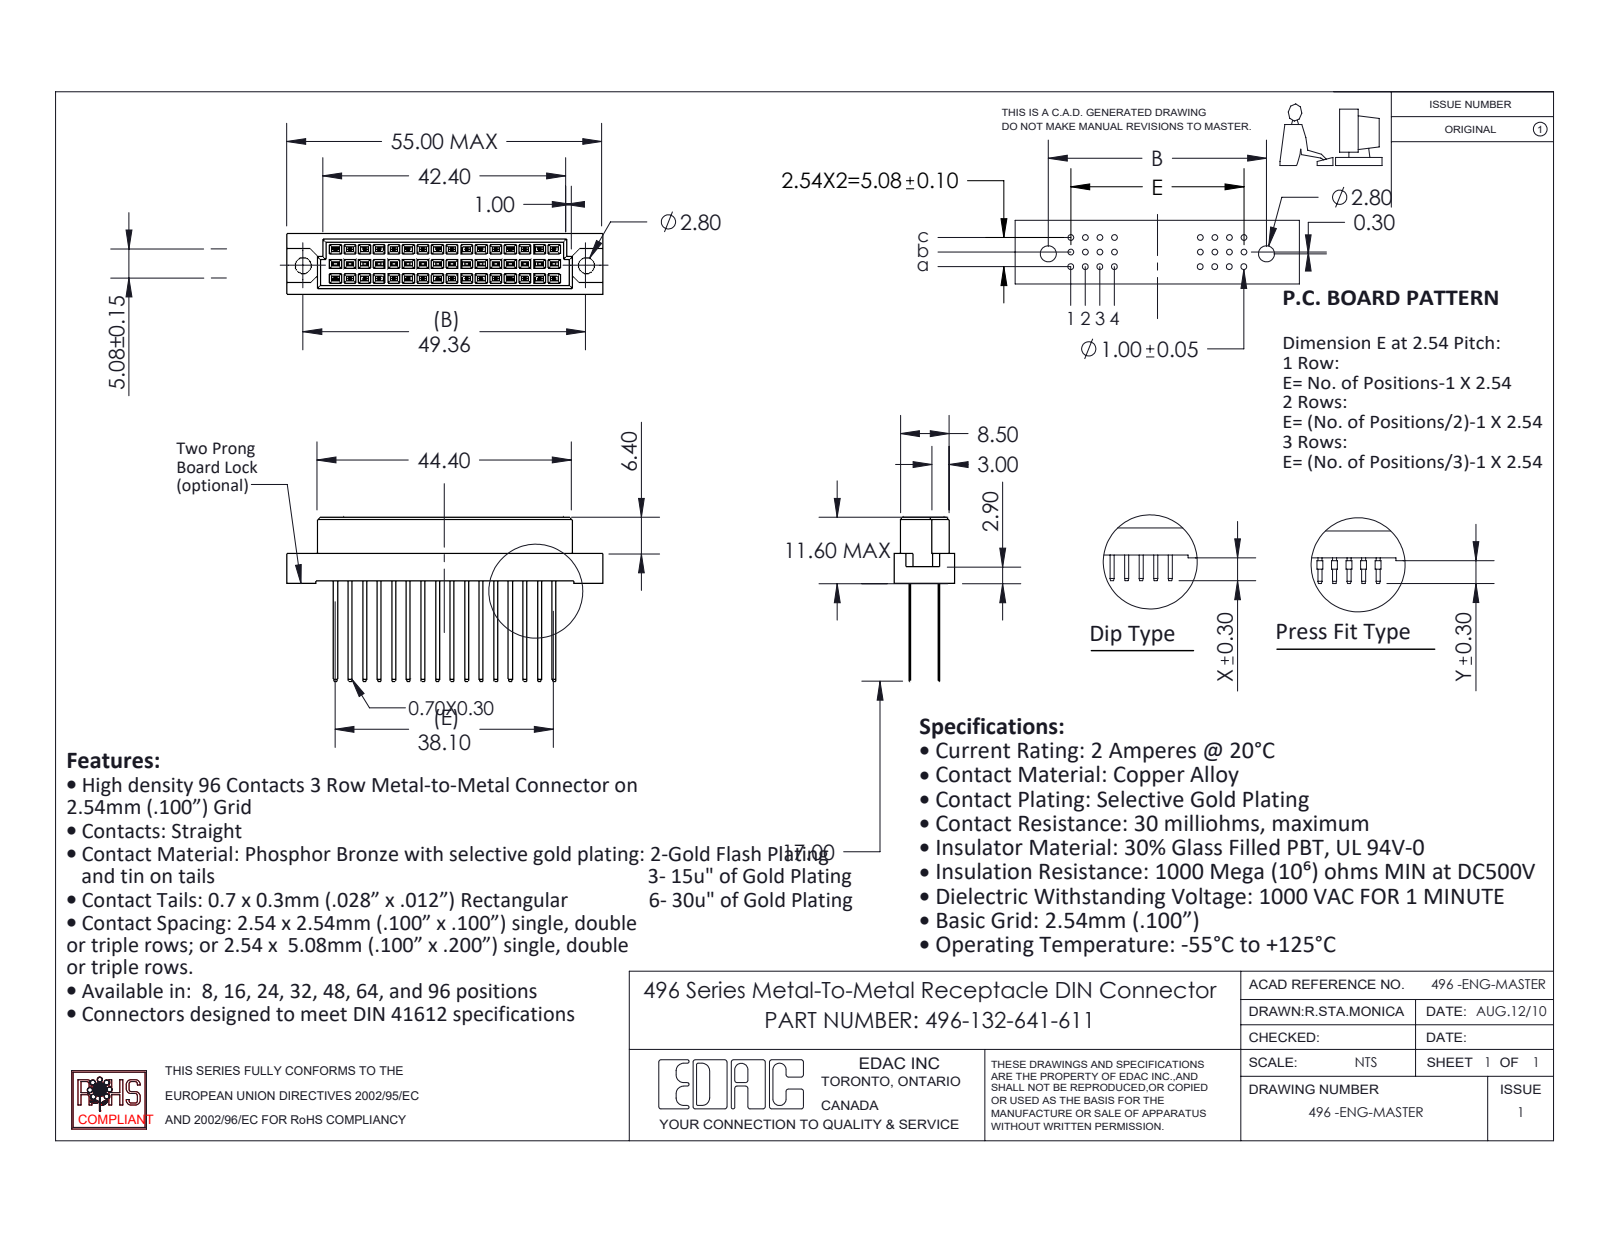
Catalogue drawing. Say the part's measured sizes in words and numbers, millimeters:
The part is named "496-132-641-611; 496-290_41; 496 Part_48". Its 3-D file was written by "SolidWorks 2020 (CONFIG_CONTROL_DESIGN)". It is 33 solids with 986 faces: 982 planar, 4 cylindrical and 0 other. Overall it measures 55 by 28.6 by 10.6 millimeters. Its volume is 4 732 cubic millimeters and its surface area 5 580 square millimeters. Round holes: 2 of diameter 2.8. The main face-to-face distances are 5.08, 2.54, 2.61, 2.91, 7.69, 7.99, 1.05, 9.55, 1.56, 1.86. The hole center spacings are 49.36.
